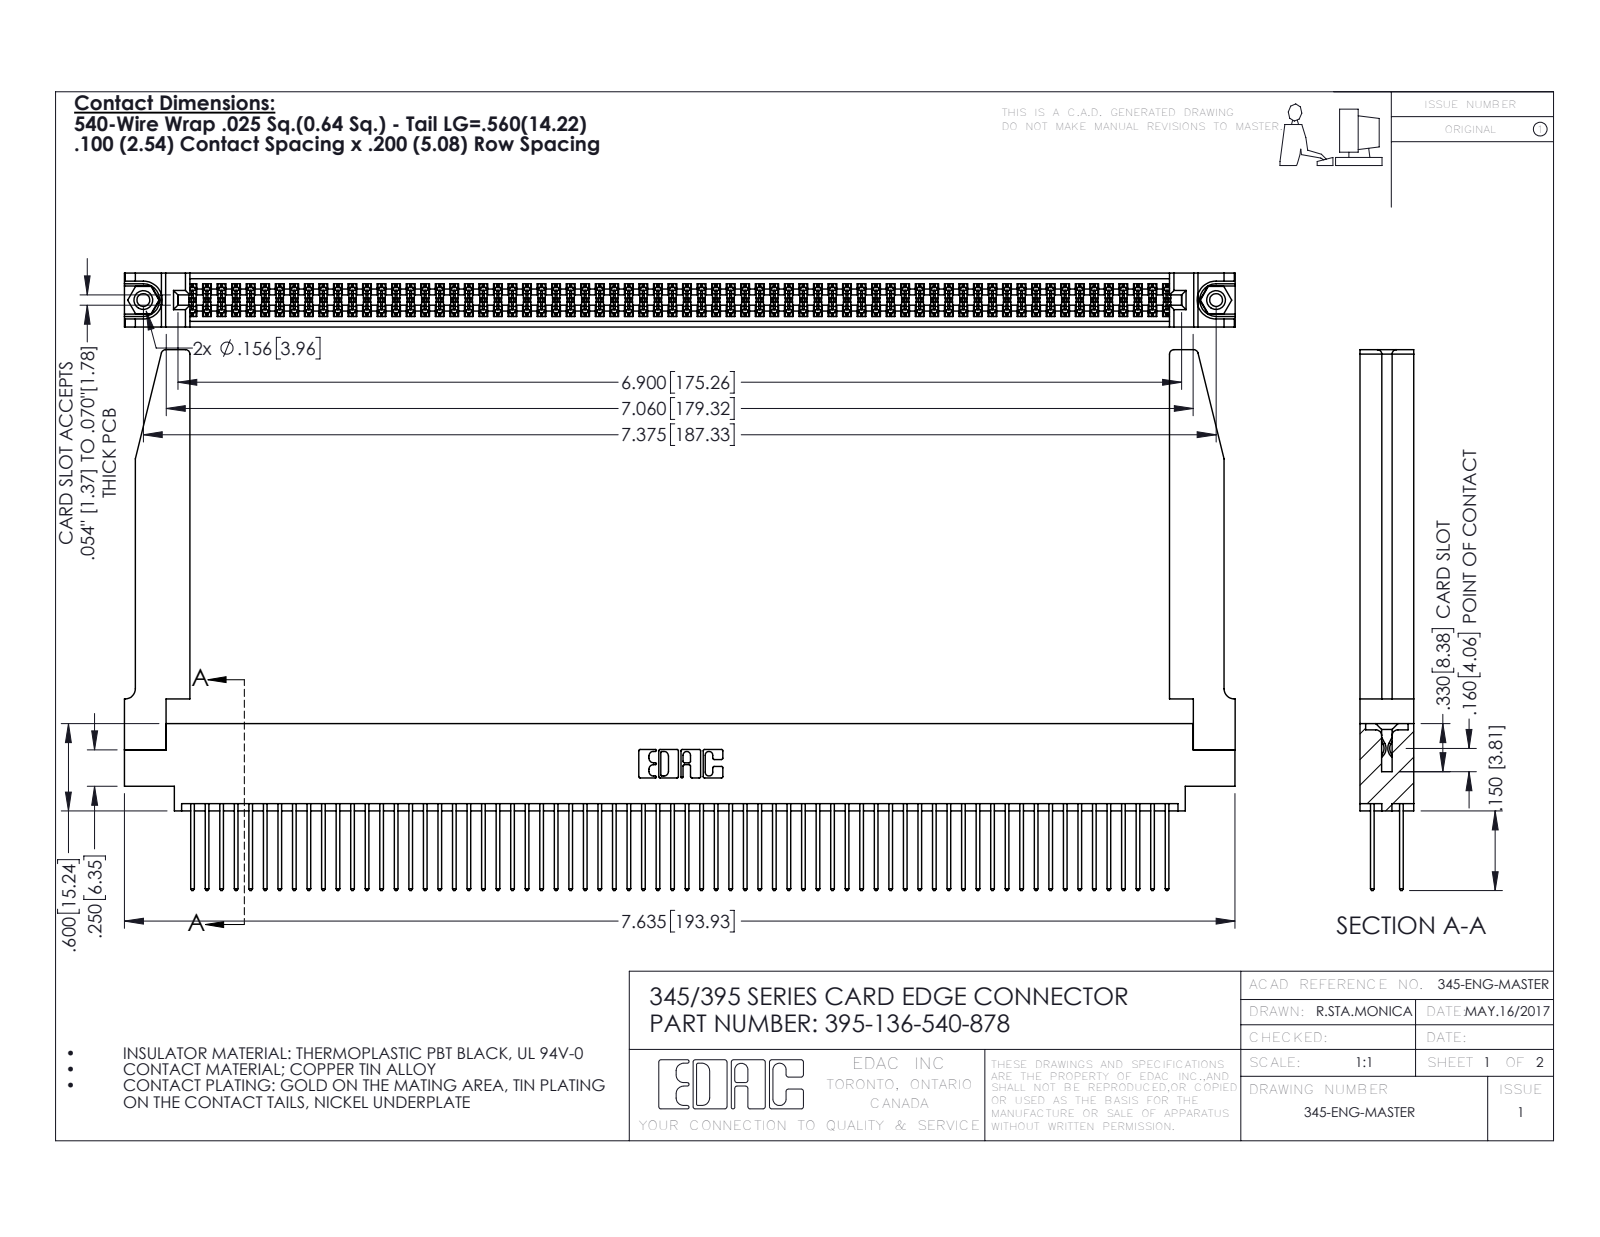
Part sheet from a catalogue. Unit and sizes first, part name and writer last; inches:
Units: inches
Overall size (bounding box): 7.636 × 3.717 × 0.37
Round holes (diameter × count): ⌀0.089 ×2, ⌀0.125 ×2, ⌀0.156 ×2, ⌀0.064 ×1
Round bosses / shafts (diameter × count): ⌀0.155 ×2
Partial cylindrical surfaces — rounded edges, fillets, slot ends (radius × count): R0.006 ×204, R0.01 ×136, R0.01 ×22, R0.03 ×8, R0.007 ×6, R0.031 ×6, R0.026 ×3, R0.014 ×2
Main face-to-face distances: 0.072, 0.298, 0.37, 0.098, 0.272, 0.025, 0.2, 0.225, 0.175, 0.149
Hole centre spacings: 0.27, 7.139, 7.375
Volume: 1.663 in³ · Surface area: 59.95 in²
Bodies: 141 solids, 7164 faces (4714 planar, 2398 cylindrical, 52 other)
Part name (STEP PRODUCT): 345-220-078_345-220-078; 345-292-001_345-293-140; 345-250-001_345-250-001-102; 395-136-540-878 (+1 more)
STEP written by: SolidWorks 2016 (CONFIG_CONTROL_DESIGN)
